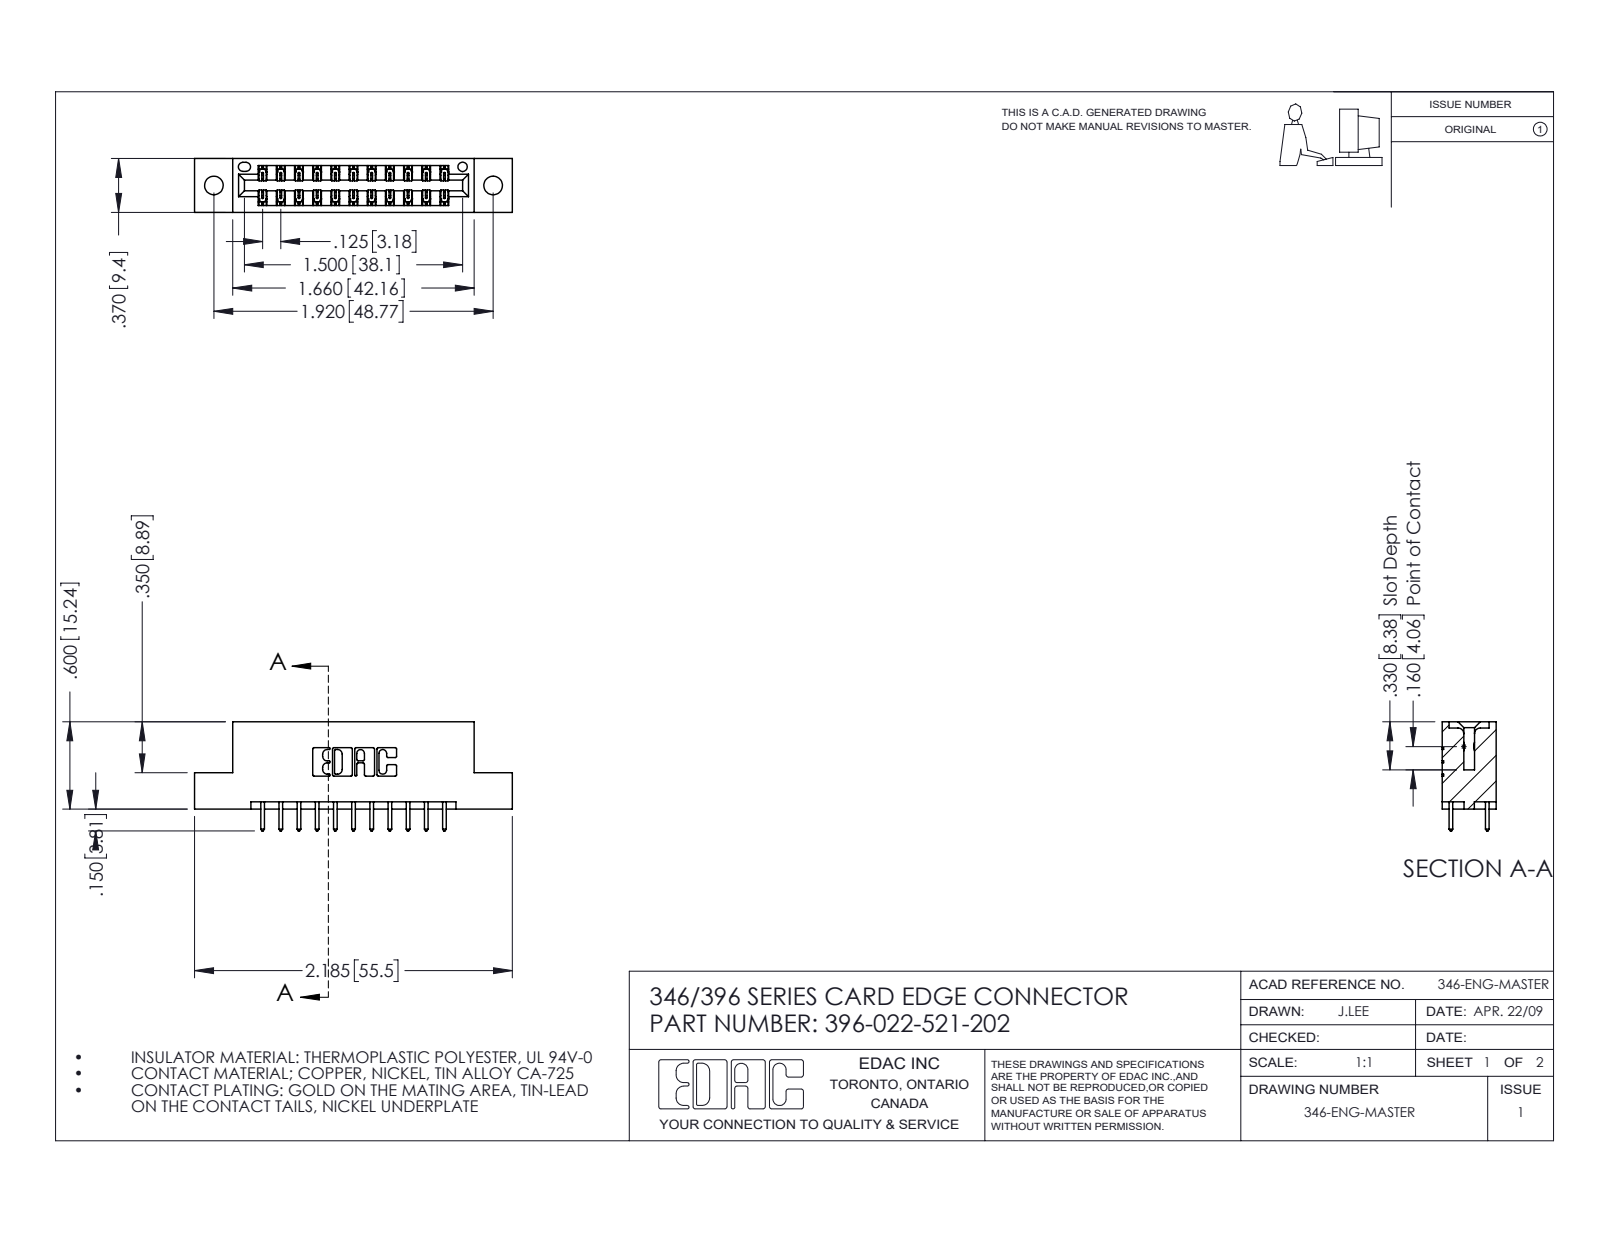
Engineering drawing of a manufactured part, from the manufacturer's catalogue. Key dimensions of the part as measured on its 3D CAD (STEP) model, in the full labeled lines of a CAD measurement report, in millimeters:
Part name (STEP PRODUCT): 345-292-001_345-293-121; 396-022-521-202; 346 Part_Flush Mounting Lugs - 0.128 Dia
STEP written by: SolidWorks 2016 (CONFIG_CONTROL_DESIGN)
Units: millimetres
Bodies: 23 solids, 1266 faces (846 planar, 420 cylindrical, 0 other)
Overall size (bounding box): 55.5 × 19.1 × 9.4
Volume: 5 130 mm³ · Surface area: 6 228 mm²
Round holes (diameter × count): ⌀3.3 ×2, ⌀1.6 ×1
Partial cylindrical surfaces — rounded edges, fillets, slot ends (radius × count): R0.2 ×33, R0.3 ×22, R0.3 ×22, R0.2 ×6, R0.8 ×6, R0.7 ×3, R0.4 ×2, R0.6 ×2
Main face-to-face distances: 6.4, 1.2, 8.2, 9.4, 1.8, 7.6, 0.6, 7, 3.8, 5.6
Hole centre spacings: 6.2, 43.6, 48.8
